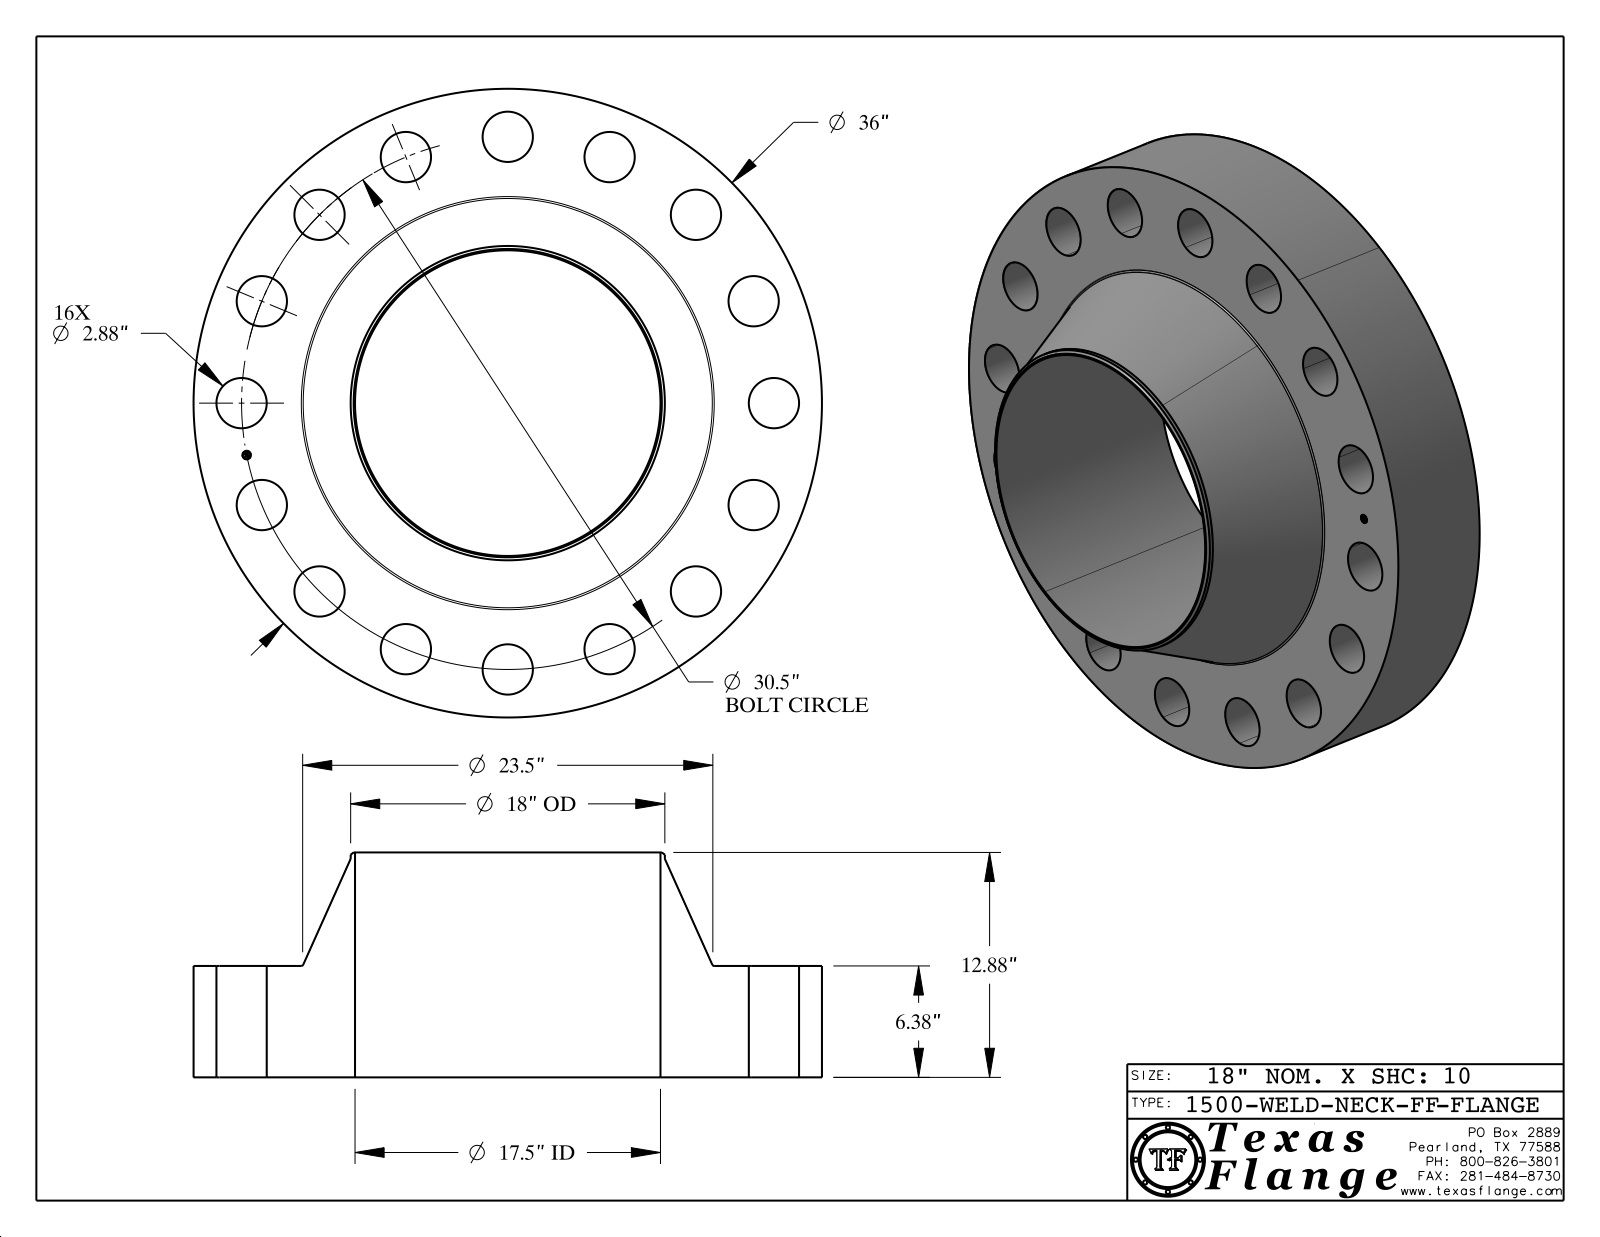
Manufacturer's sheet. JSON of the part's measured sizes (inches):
{"part_name": "1500-WELD-NECK-FF", "step_written_by": "CATIA V5 STEP AP214 (AUTOMOTIVE_DESIGN)", "units": "inches", "bodies": {"solids": 1, "faces": 432, "planar": 368, "cylindrical": 58, "other": 6}, "overall_size": [36, 36, 12.88], "volume_in3": 4910, "surface_area_in2": 3973, "round_holes": [[2.88, 16], [0.495, 1], [17.5, 1]], "round_bosses_or_shafts": [[0.03, 8], [36, 1], [18, 1], [0.39, 1]], "face_to_face_distances": [6.38, 12.88, 6.5, 6.365, 0.015, 6.515, 0.148, 0.145, 0.027, 0.096], "hole_center_spacings": [5.95, 16.945, 29.914, 15.25, 11.672, 11.672, 15.25, 21.567]}
